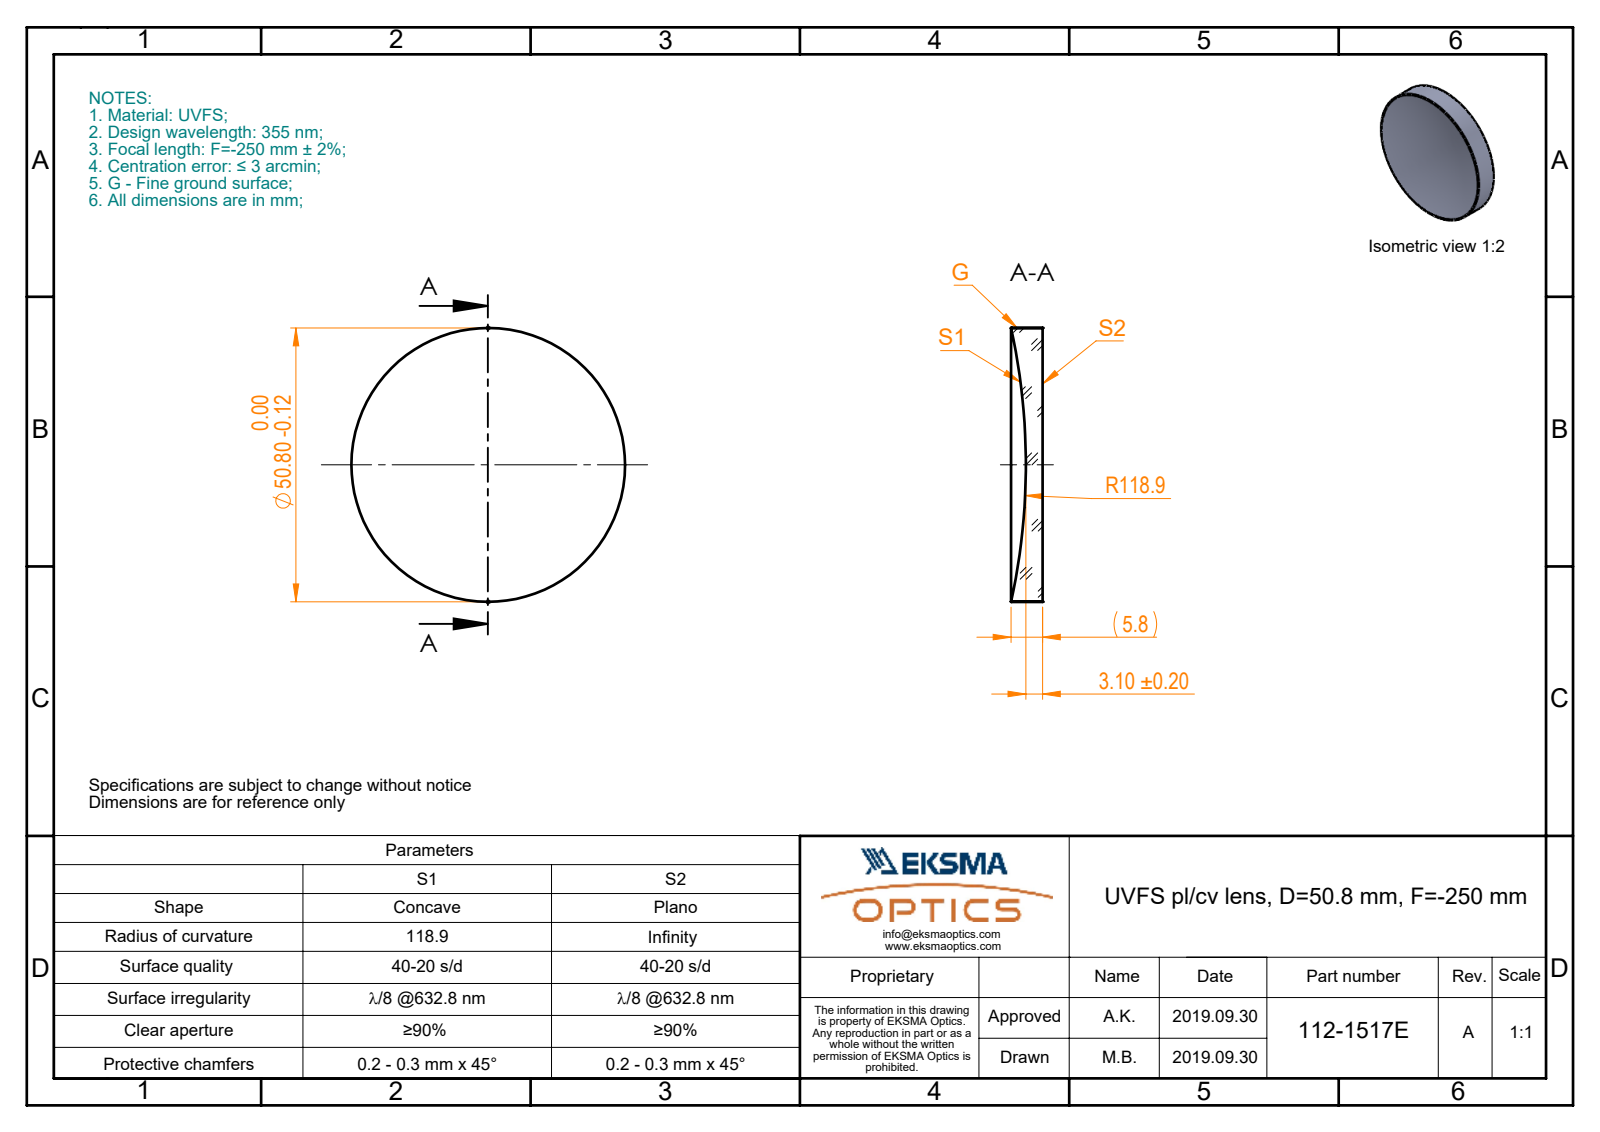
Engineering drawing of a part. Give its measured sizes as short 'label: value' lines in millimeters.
name: 112-1517E UVFS pl-cv 50.8 F-250
written by: SolidWorks 2019 (CONFIG_CONTROL_DESIGN)
unit: mm
bodies: 1 solid, 4 faces (1 planar, 2 cylindrical, 1 other)
size: 50.8 × 50.8 × 5.84
volume: 9 051 mm³; area: 5 009 mm²
bosses: 1× ⌀50.8
